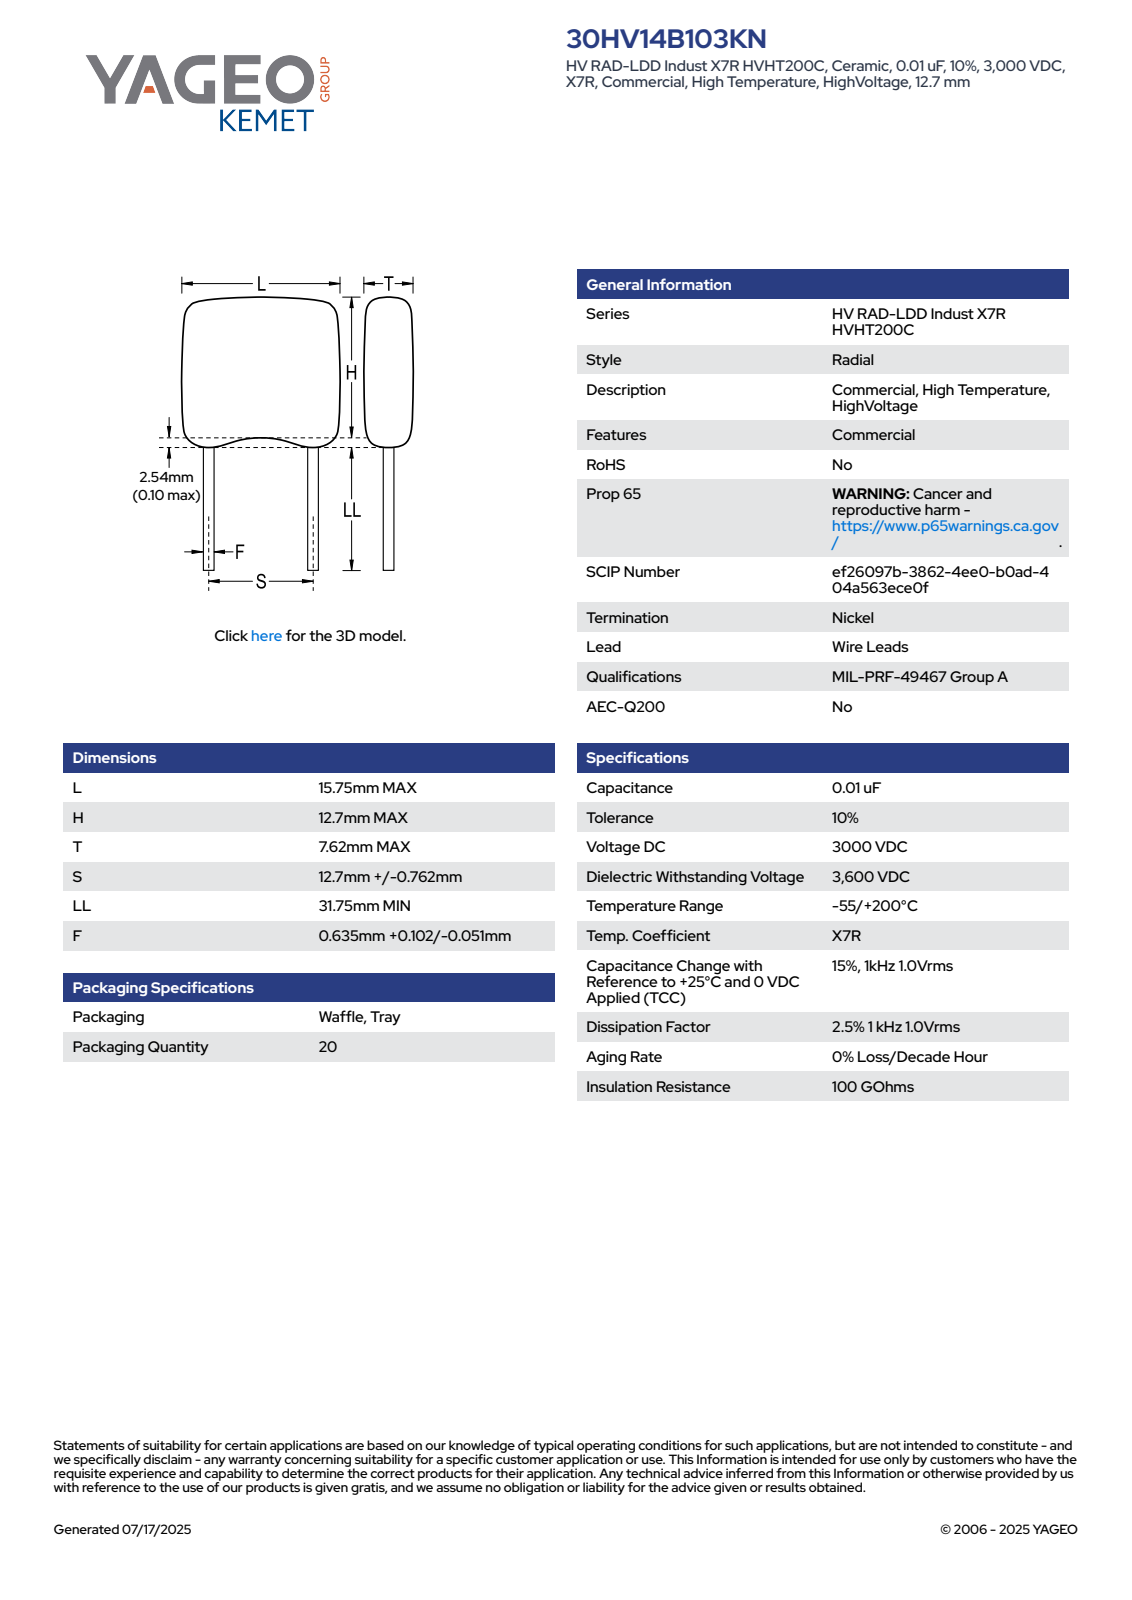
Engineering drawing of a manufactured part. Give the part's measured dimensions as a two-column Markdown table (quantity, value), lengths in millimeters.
| quantity | value |
| --- | --- |
| part name | CCRM_RCST_HV14_L15.75H12.7T7.62S12.7LL31.75F0.737 |
| STEP written by | SolidWorks 2021 (AUTOMOTIVE_DESIGN) |
| units | millimeters |
| bodies | 4 solids, 94 faces (66 planar, 18 cylindrical, 10 other) |
| overall size | 17.45 × 15.75 × 7.62 |
| volume | 1 581 mm³ |
| surface area | 872 mm² |
| round bosses / shafts (diameter × count) | 0.74 × 2 |
| partial cylindrical surfaces (radius × count) | 1 × 8, 0.5 × 4 |
| main face-to-face distances | 7.62, 15.75, 14.28, 3.17, 17.45, 11.5, 8.33, 5.95, 6.33, 7.95 |
